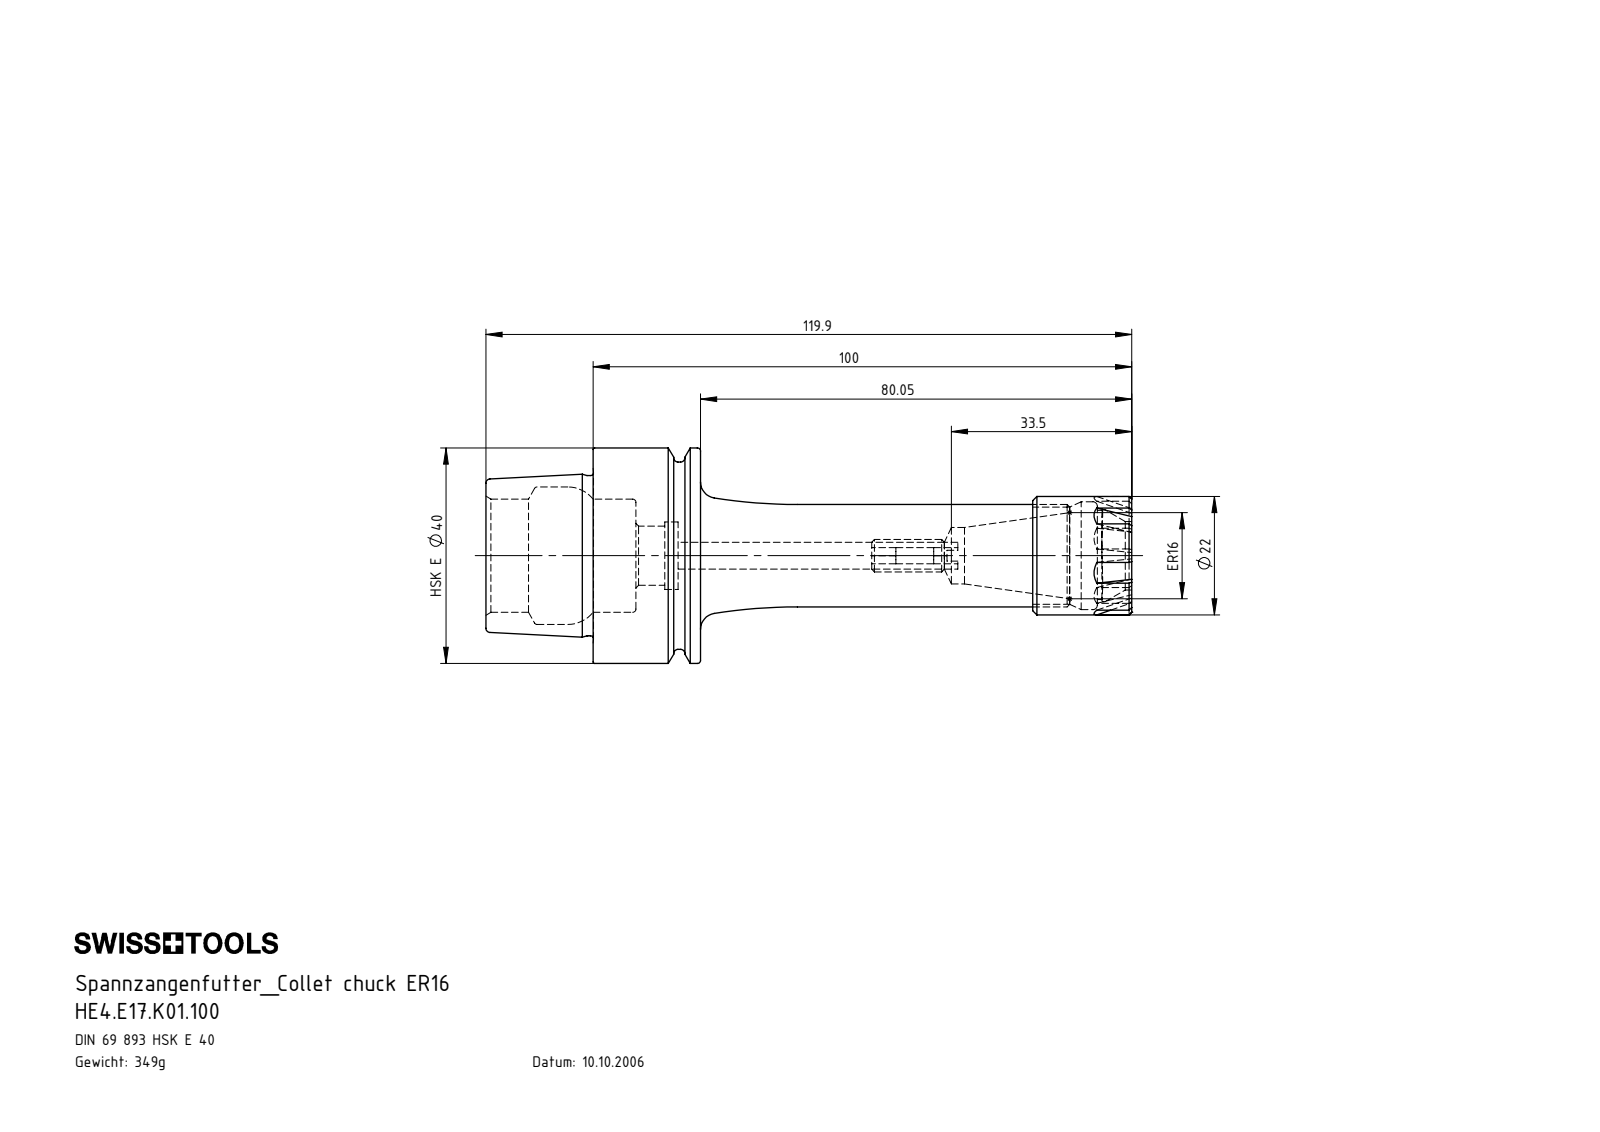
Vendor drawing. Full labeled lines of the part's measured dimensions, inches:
Part name (STEP PRODUCT): E17-ER1.001.018; ERU-AN2.K01.016_A; HE4.E17.K01.100; HE4-E17.K01.100_A_Fertigbearbeitung
STEP written by: SolidWorks 2017 (CONFIG_CONTROL_DESIGN)
Units: inches
Bodies: 3 solids, 181 faces (66 planar, 41 cylindrical, 74 other)
Overall size (bounding box): 4.72 × 1.575 × 1.575
Volume: 2.711 in³ · Surface area: 28.21 in²
Round holes (diameter × count): ⌀0.118 ×1, ⌀0.197 ×1, ⌀0.413 ×1, ⌀0.433 ×1, ⌀0.492 ×1, ⌀0.5 ×1, ⌀0.709 ×1, ⌀0.787 ×1, ⌀0.827 ×1, ⌀1.004 ×1
Round bosses / shafts (diameter × count): ⌀1.575 ×1, ⌀1.368 ×1, ⌀1.17 ×1, ⌀0.866 ×1, ⌀0.748 ×1, ⌀0.236 ×1
Partial cylindrical surfaces — rounded edges, fillets, slot ends (radius × count): R0.303 ×2
Main face-to-face distances: 0.785, 0.472, 0.313, 0.783, 1.096, 1.569, 4.72, 3.937, 3.624, 3.152
